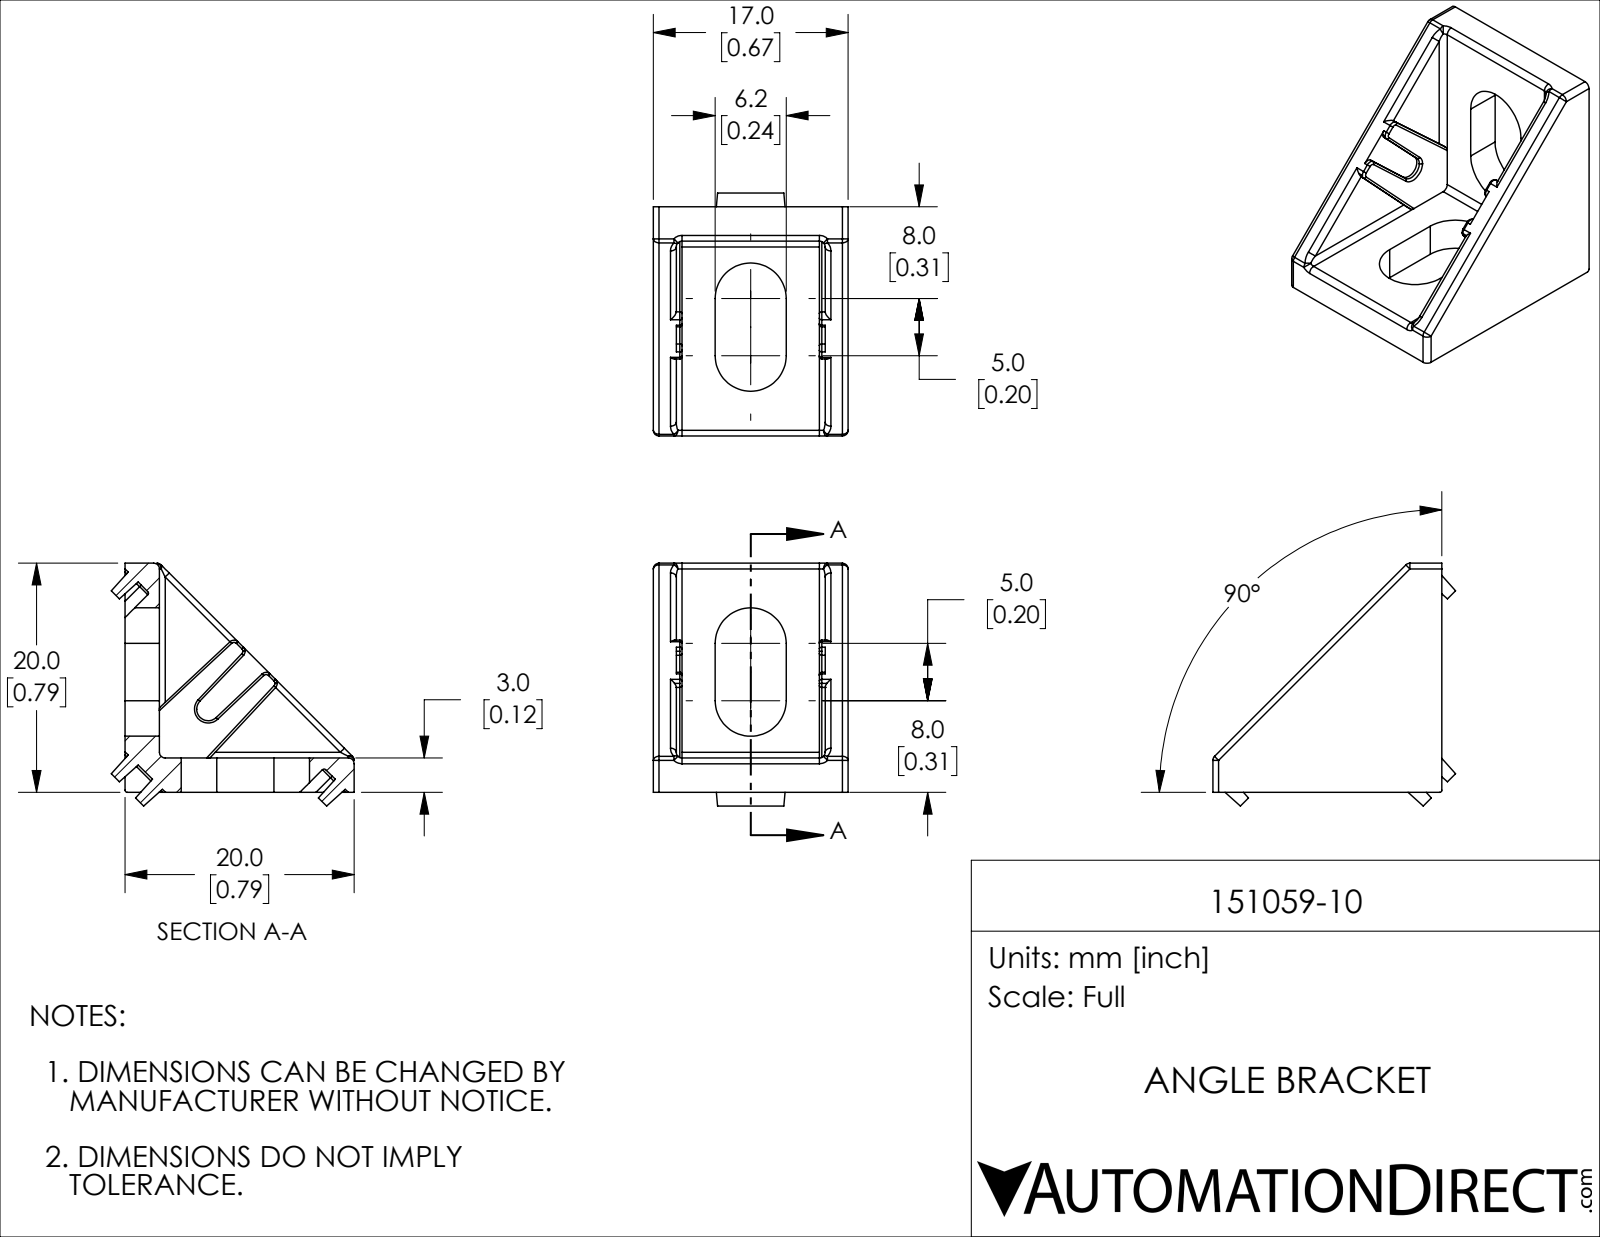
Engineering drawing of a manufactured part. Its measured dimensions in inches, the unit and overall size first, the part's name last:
Units: inches
Overall size (bounding box): 0.835 × 0.835 × 0.669
Partial cylindrical surfaces — rounded edges, fillets, slot ends (radius × count): R0.02 ×21, R0.008 ×17, R0.039 ×4, R0.122 ×4, R0.039 ×1
Main face-to-face distances: 0.669, 0.118, 0.079, 0.591, 0.787, 0.098, 0.571, 0.02, 0.492, 0.512
Volume: 0.122 in³ · Surface area: 3.385 in²
Bodies: 1 solid, 160 faces (61 planar, 66 cylindrical, 33 other)
Part name (STEP PRODUCT): 151059-10
STEP written by: SolidWorks 2024 (CONFIG_CONTROL_DESIGN)
